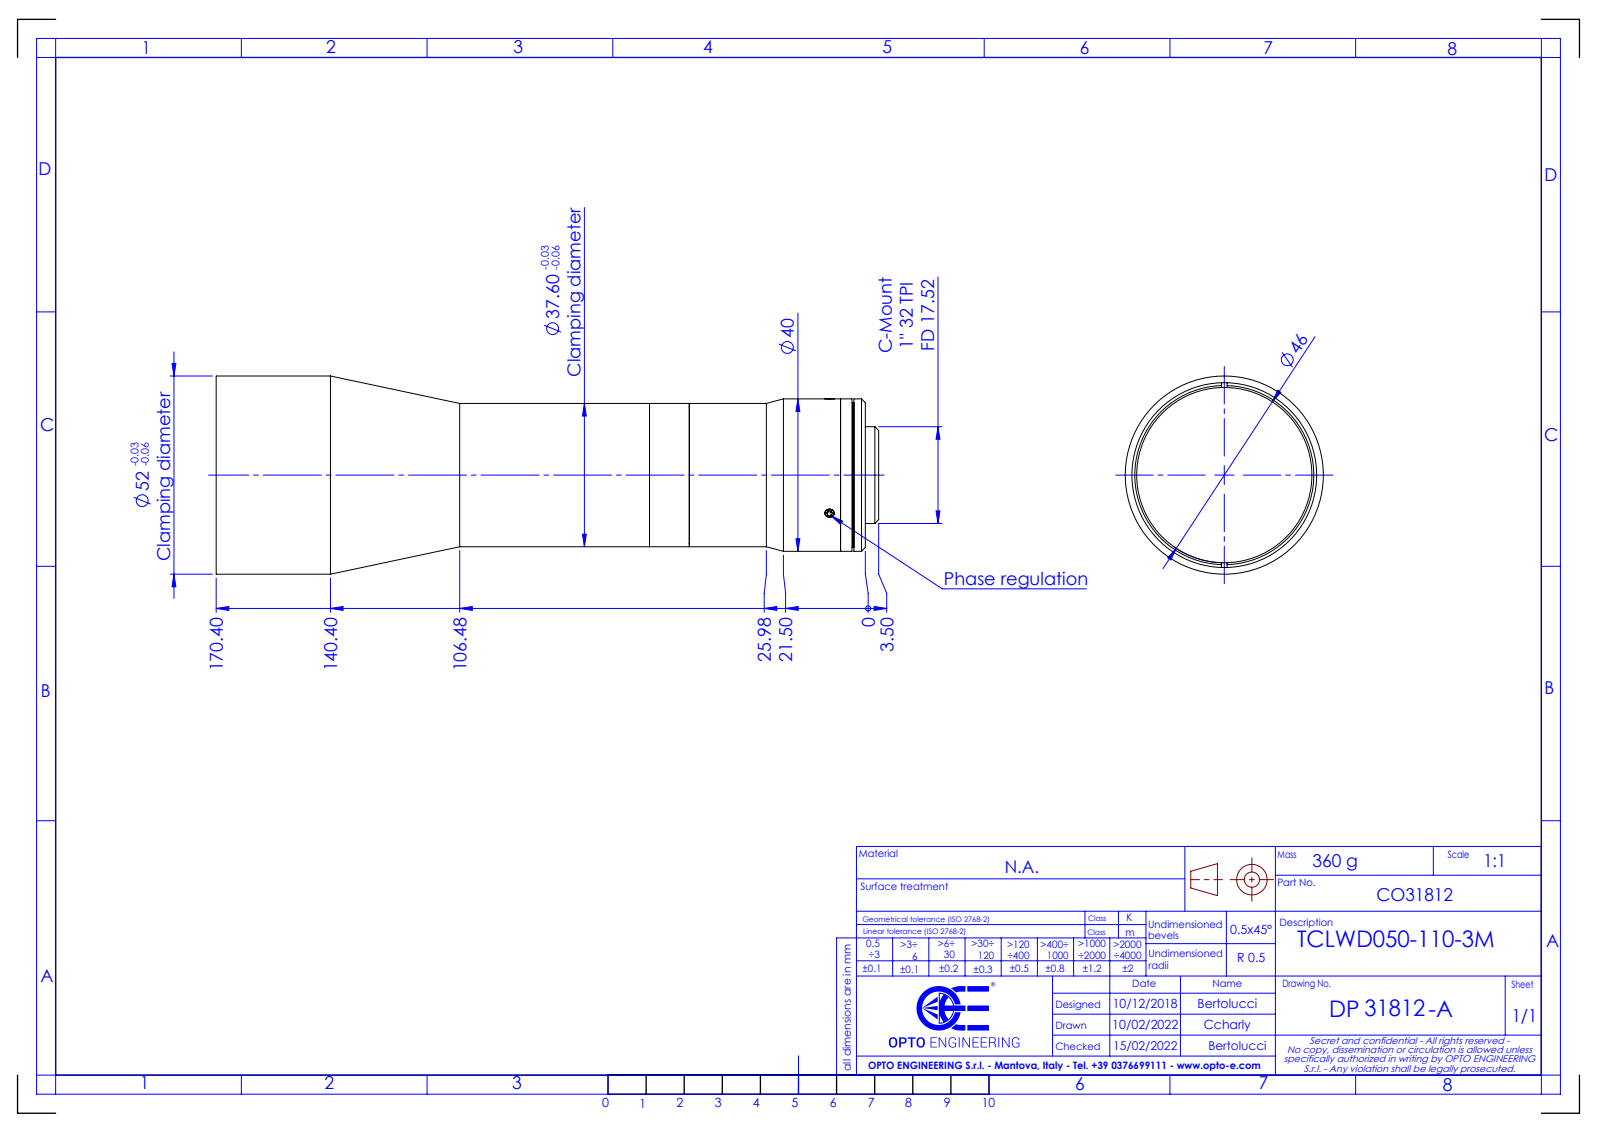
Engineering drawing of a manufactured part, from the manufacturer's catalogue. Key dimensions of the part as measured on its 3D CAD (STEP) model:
Part name (STEP PRODUCT): DP31812-A_TCLWD050-110-3M
STEP written by: SolidWorks 2021 (CONFIG_CONTROL_DESIGN)
Units: millimetres
Bodies: 0 solids, 87 faces (38 planar, 30 cylindrical, 19 other)
Overall size (bounding box): 173.9 × 52 × 52
Round holes (diameter × count): ⌀2.5 ×2, ⌀22.5 ×1, ⌀25.5 ×1, ⌀32 ×1, ⌀46 ×1, ⌀48.5 ×1
Round bosses / shafts (diameter × count): ⌀52 ×1, ⌀40 ×1, ⌀37.6 ×1, ⌀25.4 ×1
Main face-to-face distances: 3.5, 3, 0.5, 42.65, 43.15, 46.15, 6.5, 39.65, 124.25, 163.9
